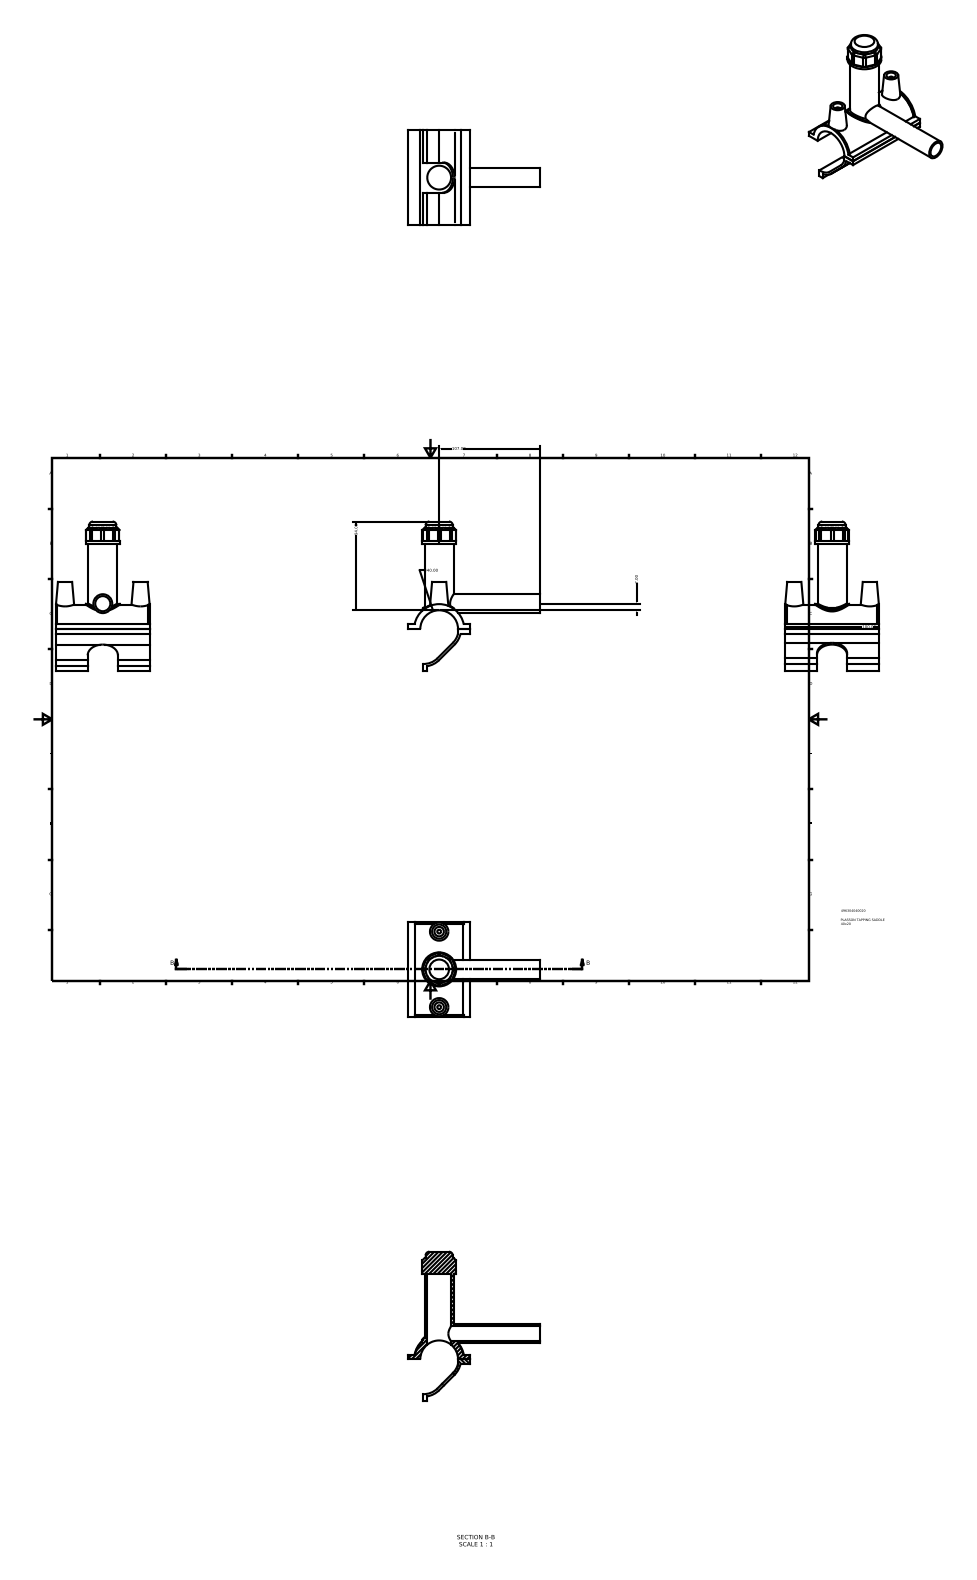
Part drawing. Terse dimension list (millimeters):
name: 496304040020
written by: Autodesk Inventor 2015 (AUTOMOTIVE_DESIGN)
unit: mm
bodies: 2 solids, 111 faces (66 planar, 32 cylindrical, 13 other)
size: 158.4 × 140 × 100
volume: 121 024 mm³; area: 61 487 mm²
holes: 2× ⌀10, 1× ⌀16, 1× ⌀25.2
bosses: 2× ⌀4, 1× ⌀36, 1× ⌀30.6, 1× ⌀28.8, 1× ⌀20
rounds: 8× R4, 2× R20.52, 2× R23.12, 1× R16, 1× R17.1, 1× R20, 1× R26, 1× R26.52
face distances: 4.95, 2.6, 9.9, 95.4, 90.45, 85.5, 100, 66, 50.4, 15.6
hole spacings: 40, 80
